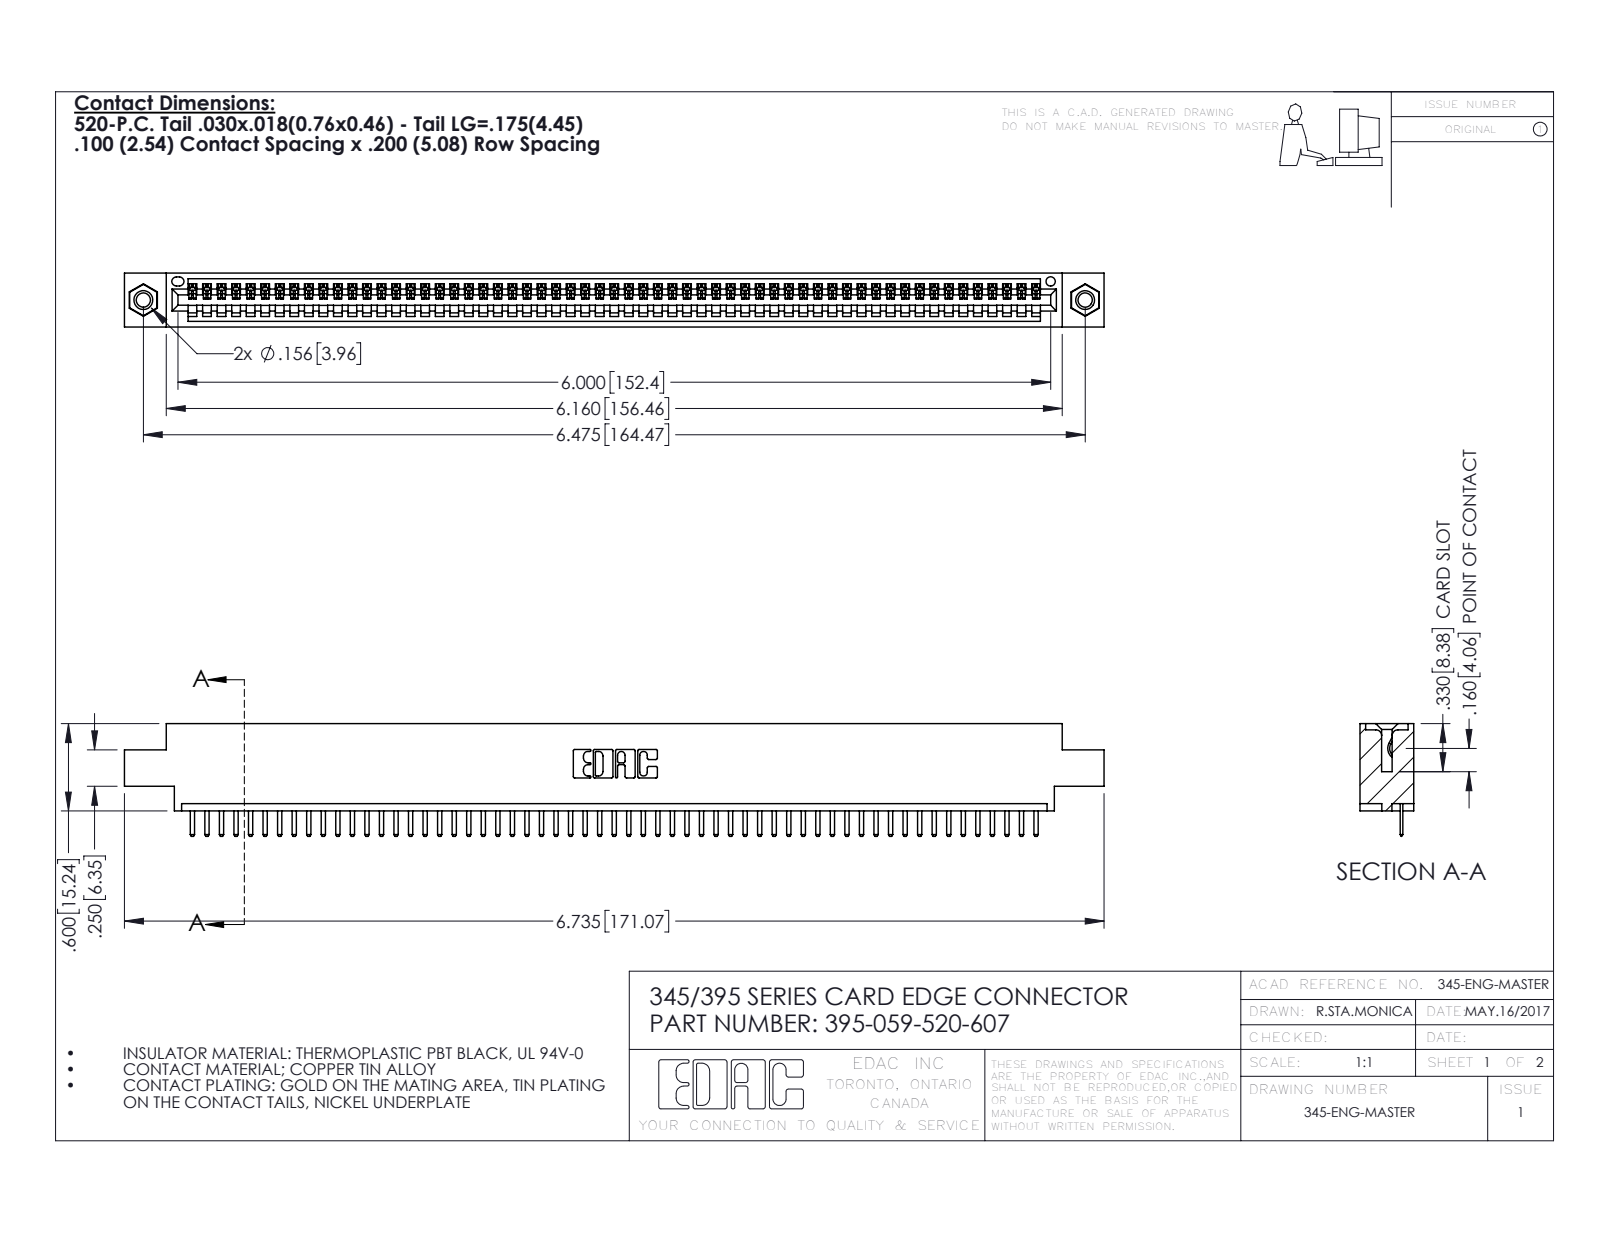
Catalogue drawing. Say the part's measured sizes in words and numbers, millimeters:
The part is named "395-059-520-607; 345-292-001_345-293-120; 345 Part_0.170 Offset - 0.156 Dia-TI; 345-250-001_345-250-005-103". Its 3-D file was written by "SolidWorks 2016 (CONFIG_CONTROL_DESIGN)". It is 62 solids with 3848 faces: 2594 planar, 1238 cylindrical and 16 other. Overall it measures 171.1 by 19.7 by 9.4 millimeters. Its volume is 16 100 cubic millimeters and its surface area 21 220 square millimeters. Round holes: 2 of diameter 2.5, 2 of diameter 3.2, 2 of diameter 4, 1 of diameter 1.6. Round bosses or shafts: 2 of diameter 3.9. Partial cylindrical surfaces (rounded edges, fillets, slot ends): 120 of radius 0.3, 118 of radius 0.2, 22 of radius 0.3, 6 of radius 0.2, 6 of radius 0.8, 3 of radius 0.7, 2 of radius 0.8, 2 of radius 1. The main face-to-face distances are 1.8, 7.6, 9.4, 5.1, 2.5, 6.9, 0.6, 5.7, 1.8, 4.4. The hole center spacings are 6.9, 158.5, 164.5.
